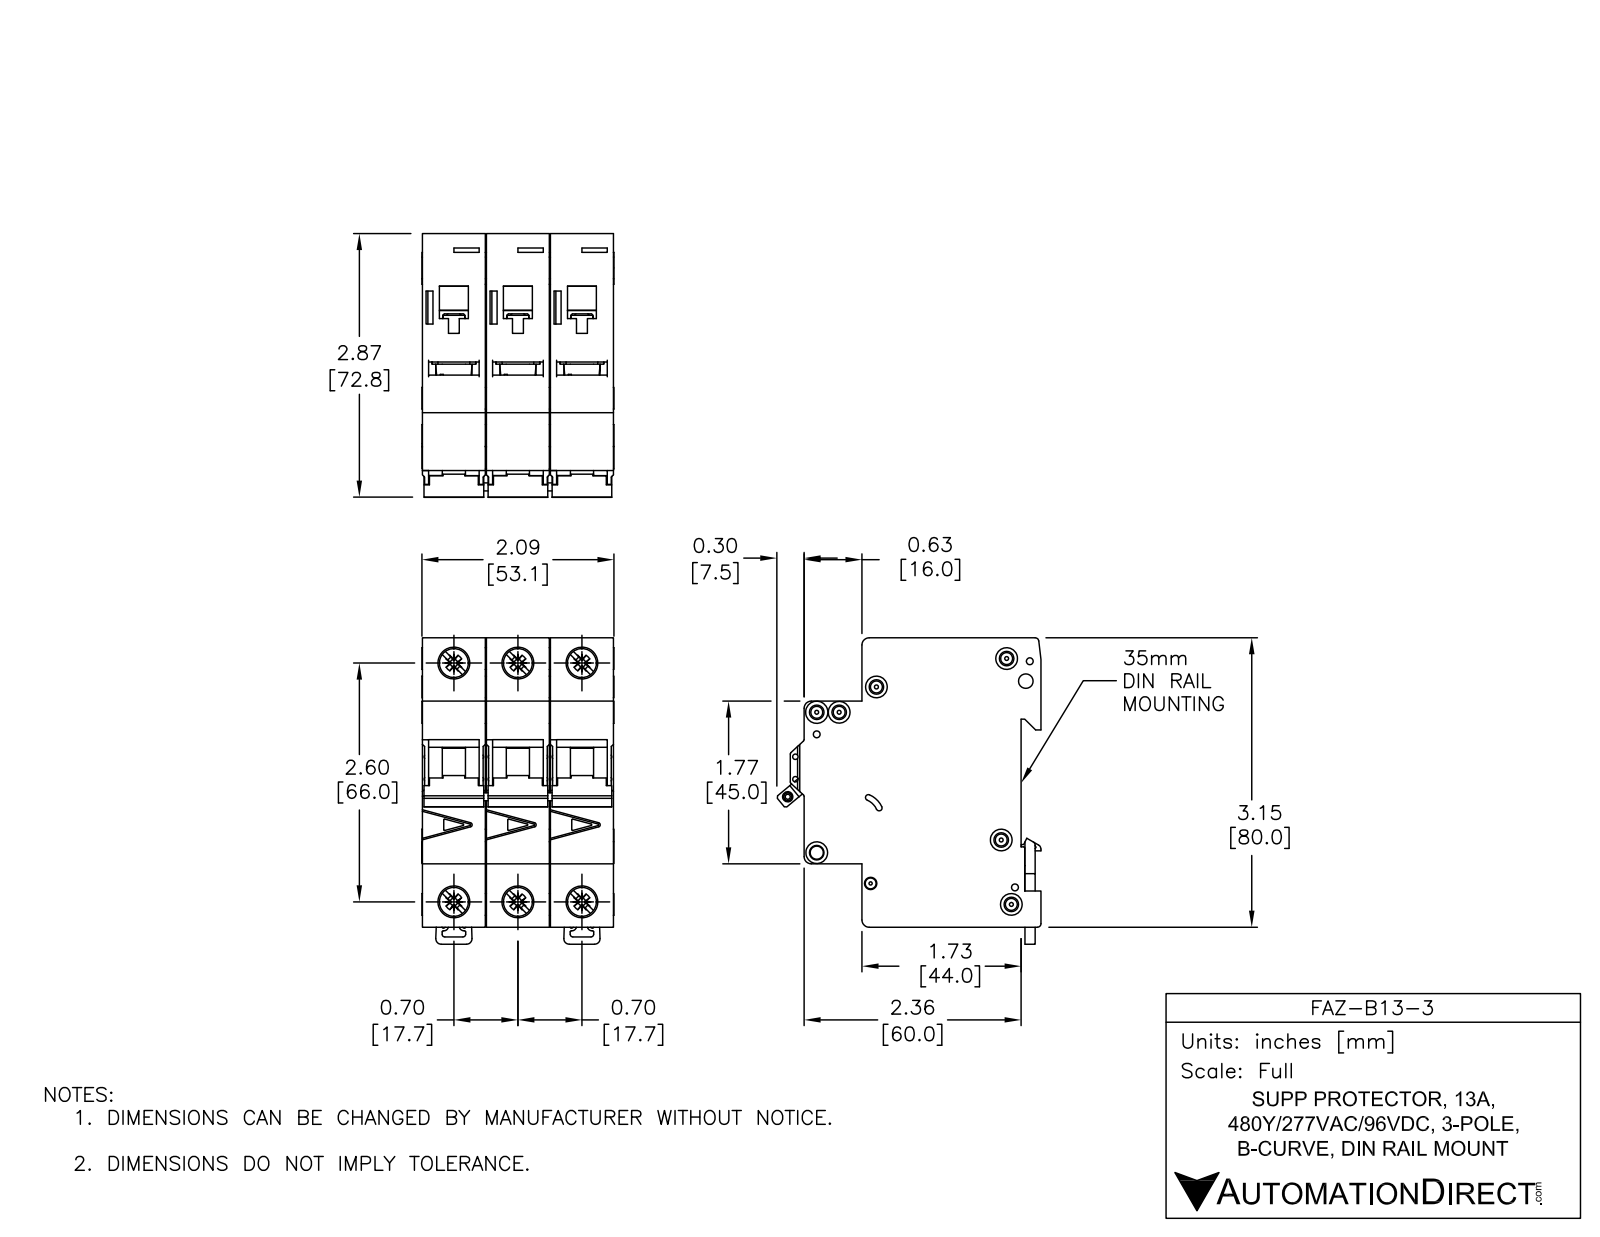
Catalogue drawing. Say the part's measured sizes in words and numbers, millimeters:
The part is named "FAZ-B13-3". Its 3-D file was written by "SolidWorks 2014 (AUTOMOTIVE_DESIGN)". It is 11 solids with 1650 faces: 697 planar, 590 cylindrical and 363 other. Overall it measures 84.78 by 73.04 by 53.1 millimeters. Its volume is 224 680 cubic millimeters and its surface area 58 052 square millimeters. Round holes: 6 of diameter 3.6, 4 of diameter 8.2, 3 of diameter 1.9, 2 of diameter 1.09, 2 of diameter 1.5, 2 of diameter 4, 2 of diameter 7.15, 1 of diameter 2.15, 1 of diameter 2.2, 1 of diameter 2.55, 1 of diameter 3.3, 1 of diameter 3.4. Round bosses or shafts: 4 of diameter 6, 3 of diameter 2.5, 2 of diameter 8.2. Partial cylindrical surfaces (rounded edges, fillets, slot ends): 68 of radius 0.25, 25 of radius 0.5, 12 of radius 1, 12 of radius 2, 11 of radius 0.2, 3 of radius 1.8, 2 of radius 0.8, 2 of radius 3. The main face-to-face distances are 17.7, 17.5, 35.4, 35.2, 52.9, 17.9, 79.48, 5.5, 49.5, 44. The hole center spacings are 17.7, 68.33, 66, 6.2, 13.64, 35.4, 74.89, 4.81.
